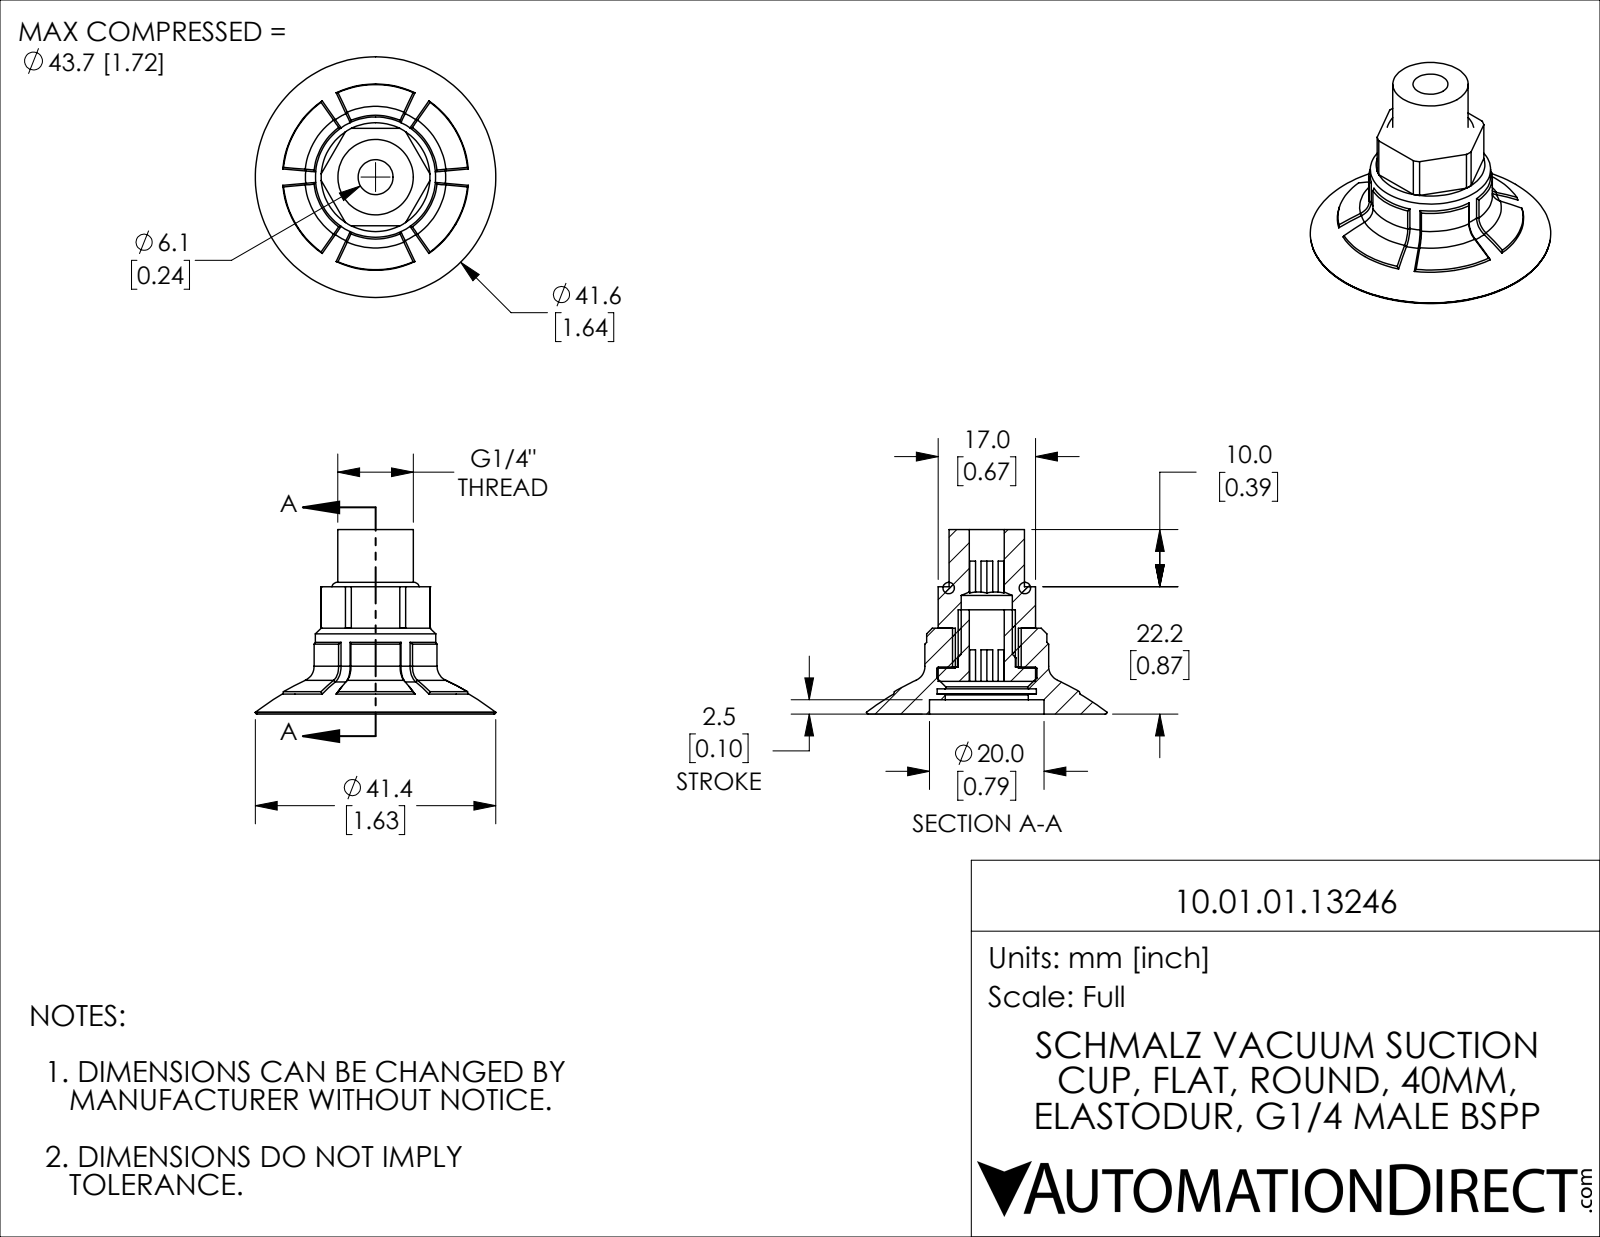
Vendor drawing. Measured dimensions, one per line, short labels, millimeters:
name: 10.01.01.13246
written by: SolidWorks 2021 (CONFIG_CONTROL_DESIGN)
unit: mm
bodies: 4 solids, 205 faces (66 planar, 41 cylindrical, 98 other)
size: 42 × 42 × 32.2
volume: 10 110 mm³; area: 7 685 mm²
holes: 1× ⌀6.1, 1× ⌀8.92, 1× ⌀10.2, 1× ⌀11, 1× ⌀14.51, 1× ⌀17.3, 1× ⌀17.5, 1× ⌀20
bosses: 1× ⌀21, 1× ⌀17, 1× ⌀13.16, 1× ⌀12, 1× ⌀10
rounds: 1× R9.5, 1× R10.8
face distances: 5.7, 2.5, 15, 5.5, 3.2, 12.5, 9.3, 17, 6.8, 8.2
